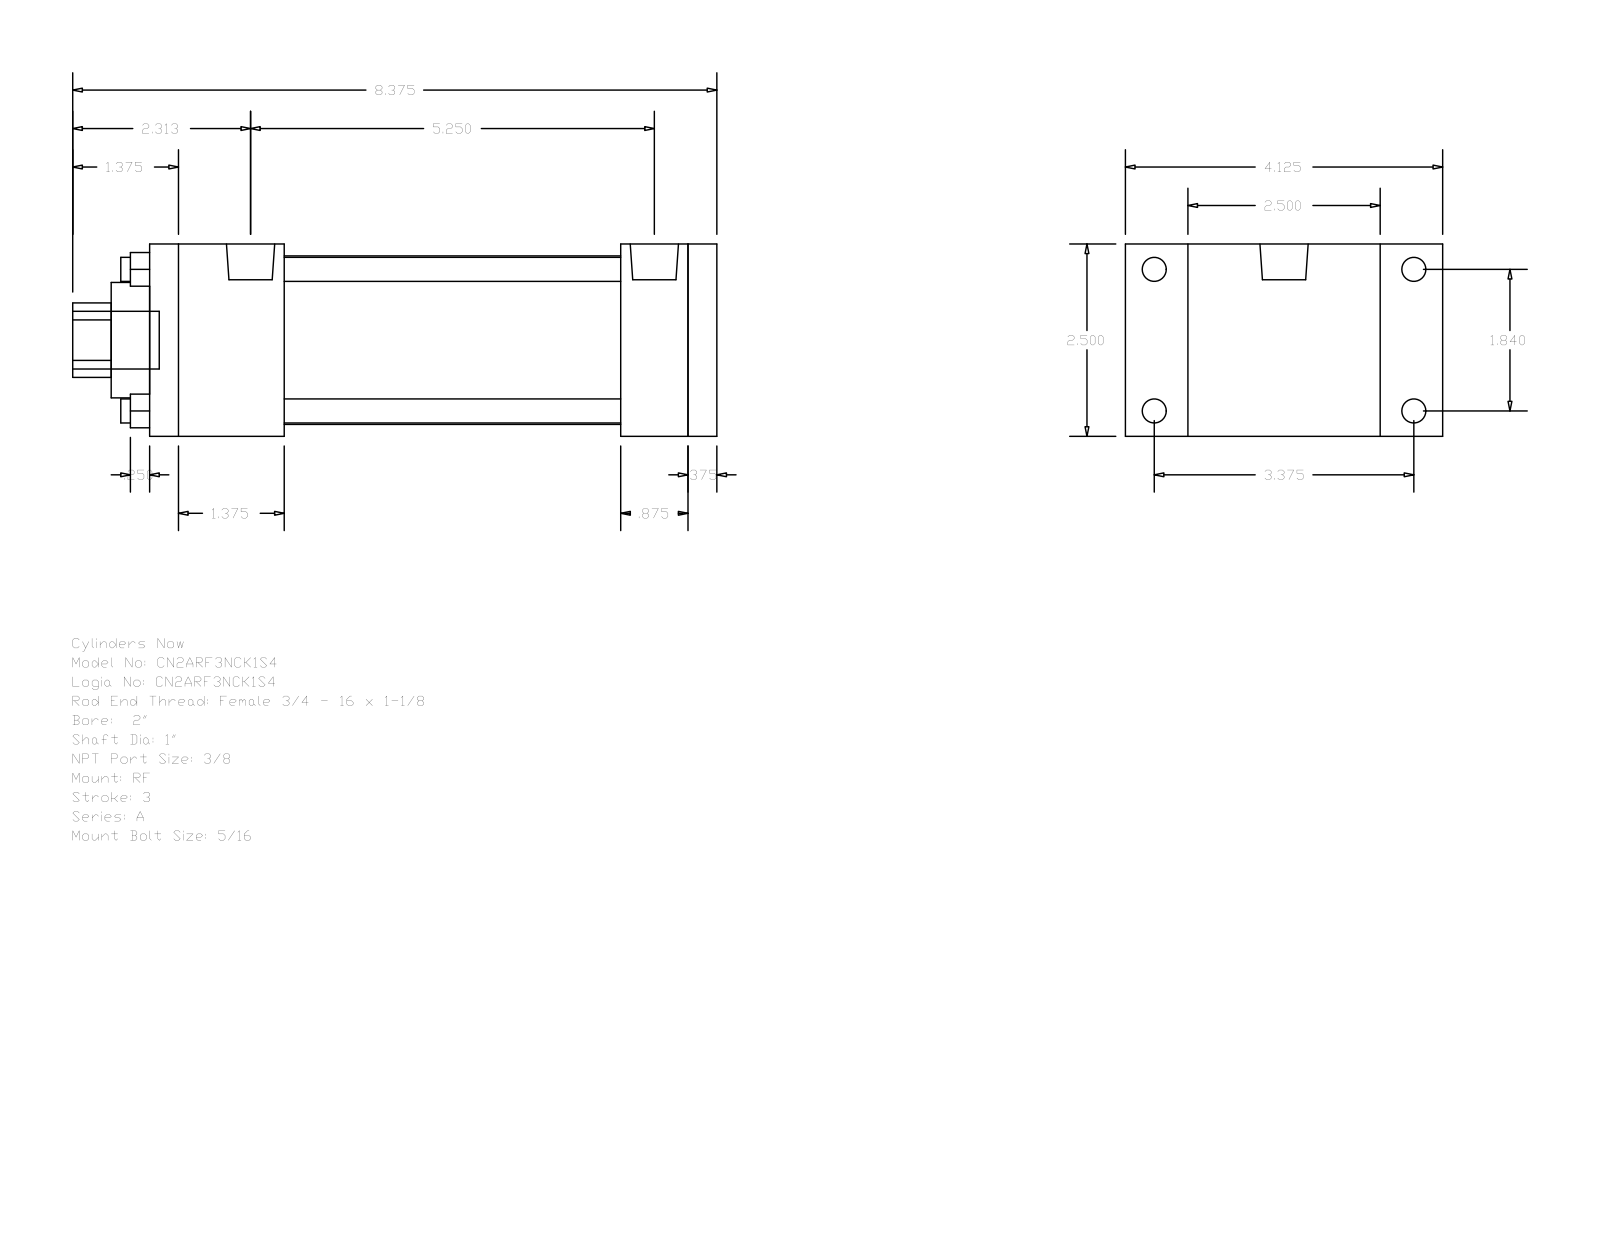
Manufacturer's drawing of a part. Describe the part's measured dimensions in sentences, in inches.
The part is named "A_RF__0200_1". Its 3-D file was written by "GSSL Pune (CONFIG_CONTROL_DESIGN)". It is 0 solids with 92 faces: 64 planar, 28 cylindrical and 0 other. Overall it measures 8.375 by 4.125 by 2.5 inches. Round holes: 4 of diameter 0.313, 1 of diameter 1, 1 of diameter 1.5, 1 of diameter 2.19. Round bosses or shafts: 4 of diameter 0.313, 4 of diameter 0.219, 2 of diameter 0.627, 1 of diameter 0.75. Partial cylindrical surfaces (rounded edges, fillets, slot ends): 1 of radius 0.484. The main face-to-face distances are 2.5, 0.375, 7.375, 7, 0.813, 1.75, 5.25, 5.625, 6.125, 4.375. The hole center spacings are 1.301, 1.84, 2.602.
